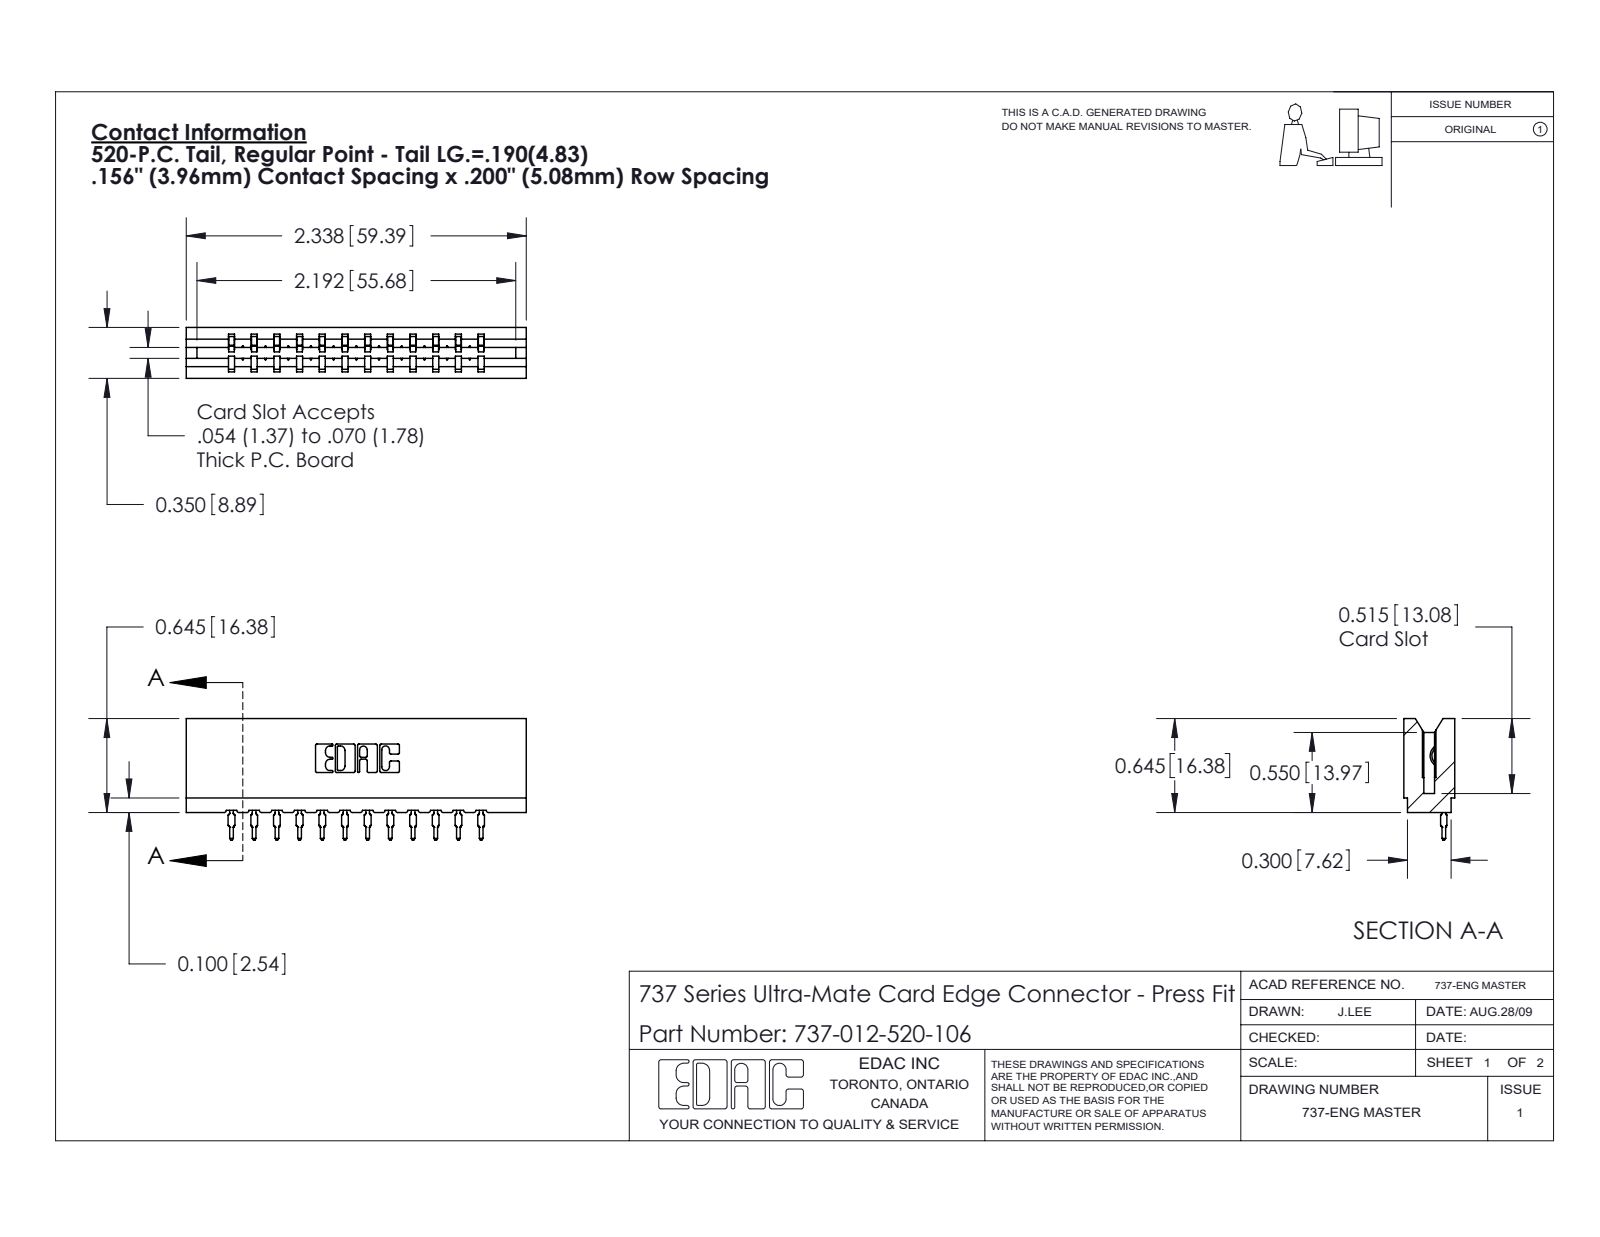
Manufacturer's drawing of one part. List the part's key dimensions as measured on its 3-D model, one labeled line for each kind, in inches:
Part name (STEP PRODUCT): 737 Part_Insulator Option - 06; 745-292-001_520; 737-012-520-106
STEP written by: SolidWorks 2020 (CONFIG_CONTROL_DESIGN)
Units: inches
Bodies: 13 solids, 1451 faces (871 planar, 268 cylindrical, 312 other)
Overall size (bounding box): 2.338 × 0.836 × 0.35
Volume: 0.361 in³ · Surface area: 11.34 in²
Partial cylindrical surfaces — rounded edges, fillets, slot ends (radius × count): R0.015 ×24, R0.021 ×24, R0.01 ×22, R0.007 ×6, R0.031 ×6, R0.005 ×4, R0.011 ×4, R0.026 ×3
Main face-to-face distances: 0.156, 0.138, 0.212, 0.35, 0.624, 0.312, 0.468, 0.78, 0.074, 0.354
